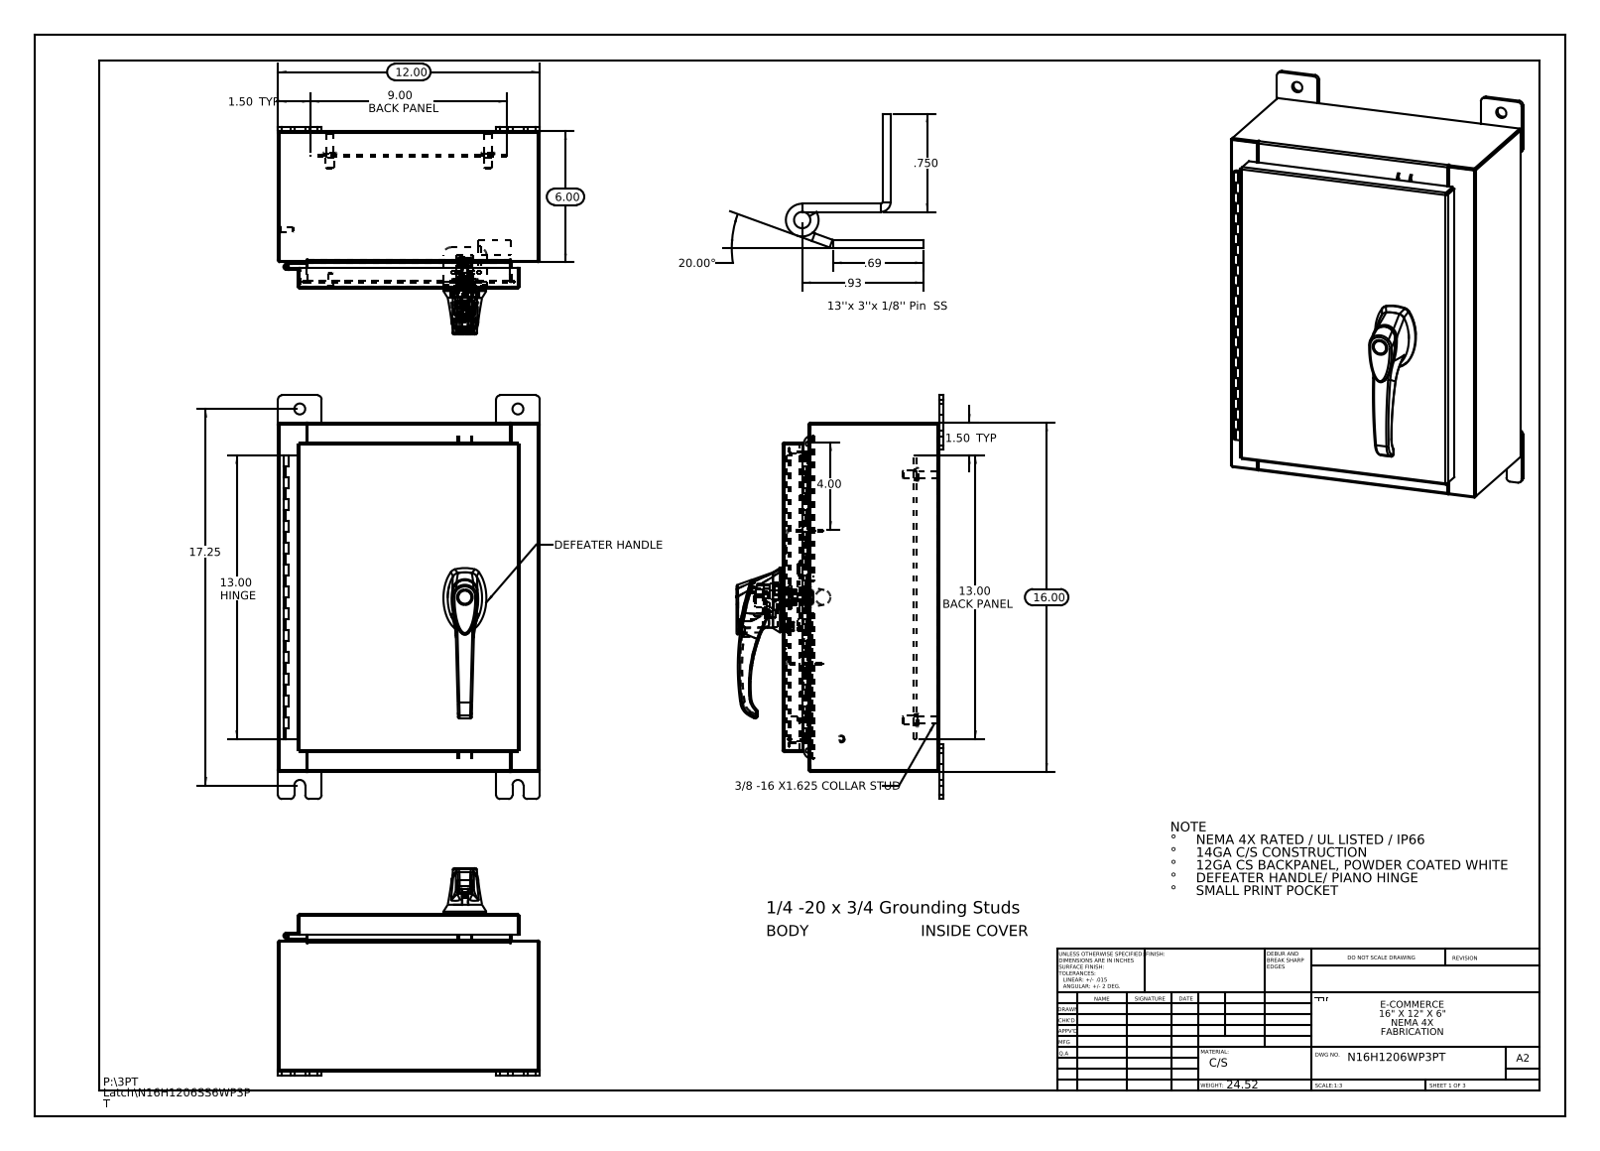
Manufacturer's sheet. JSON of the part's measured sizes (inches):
{"part_name": "012103_012102; N16H1206SS6WP3PT Backpanel; N16H1206SS6WP3PT Top; 297025 (+8 more)", "step_written_by": "SolidWorks 2013 (CONFIG_CONTROL_DESIGN)", "units": "inches", "bodies": {"solids": 31, "faces": 2204, "planar": 757, "cylindrical": 793, "other": 654}, "overall_size": [18.5, 12, 9.495], "volume_in3": 88.86, "surface_area_in2": 2168, "round_holes": [[0.5, 8], [0.25, 4], [0.138, 3], [0.161, 3], [0.079, 2], [0.203, 2], [0.313, 2], [0.437, 2], [0.125, 1], [0.125, 1], [0.197, 1], [0.276, 1]], "round_bosses_or_shafts": [[0.625, 4], [0.375, 4], [0.33, 4], [1.181, 1], [0.748, 1], [0.68, 1], [0.661, 1], [0.639, 1]], "partial_cylinders_radius": [[0.118, 37], [0.006, 33], [0.19, 24], [0.013, 20], [0.088, 18], [0.039, 15], [0.028, 12], [0.008, 6]], "face_to_face_distances": [0.075, 7.126, 11.925, 7.051, 7.201, 15.925, 5.925, 1.201, 1, 0.104], "hole_center_spacings": [3.708, 0.295, 0.625, 0.841, 1.25, 1.313, 1.32, 1.484]}
